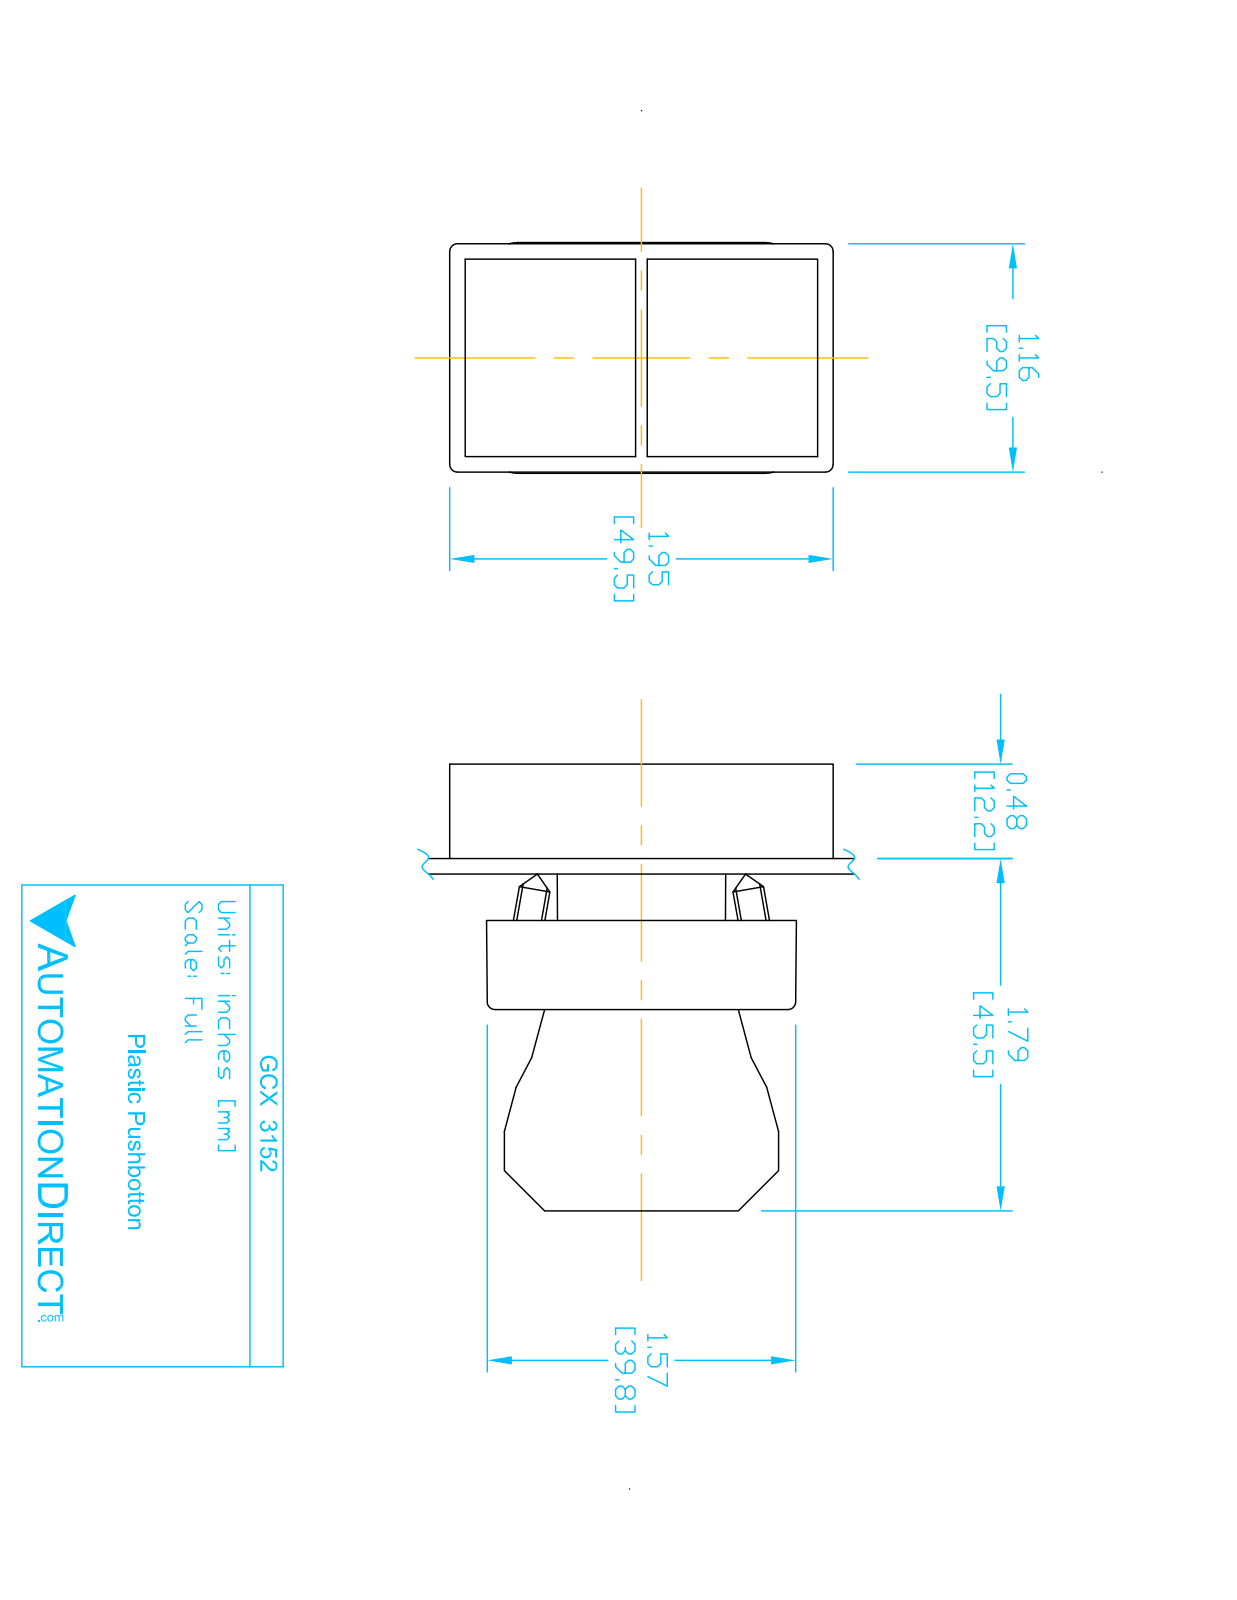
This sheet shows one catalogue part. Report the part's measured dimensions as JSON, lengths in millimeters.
{"part_name": "GCX3152 OPERATOR; ECX3029-2; ecx1040; ecx1030 (+1 more)", "step_written_by": "SolidWorks 2016 (AUTOMOTIVE_DESIGN)", "units": "millimeters", "bodies": {"solids": 8, "faces": 495, "planar": 322, "cylindrical": 144, "other": 29}, "overall_size": [56.3, 49.5, 29.9], "volume_mm3": 47880, "surface_area_mm2": 27750, "round_holes": [[2, 4], [2.2, 2], [3.1, 2], [3.3, 2], [5, 1], [18, 1], [22.3, 1], [22.6, 1]], "round_bosses_or_shafts": [[4, 2], [24, 1], [21.7, 1], [19.8, 1], [15, 1]], "partial_cylinders_radius": [[1.5, 24], [1, 12], [3.1, 12], [4, 12], [1, 4], [1.6, 2], [2, 2], [3.3, 2]], "face_to_face_distances": [0.5, 1, 13.5, 1.5, 14.7, 15.2, 15, 18.8, 30.3, 11.5], "hole_center_spacings": [6, 13.8, 25.6, 24.9, 12, 12.4, 13.7, 17.1]}
